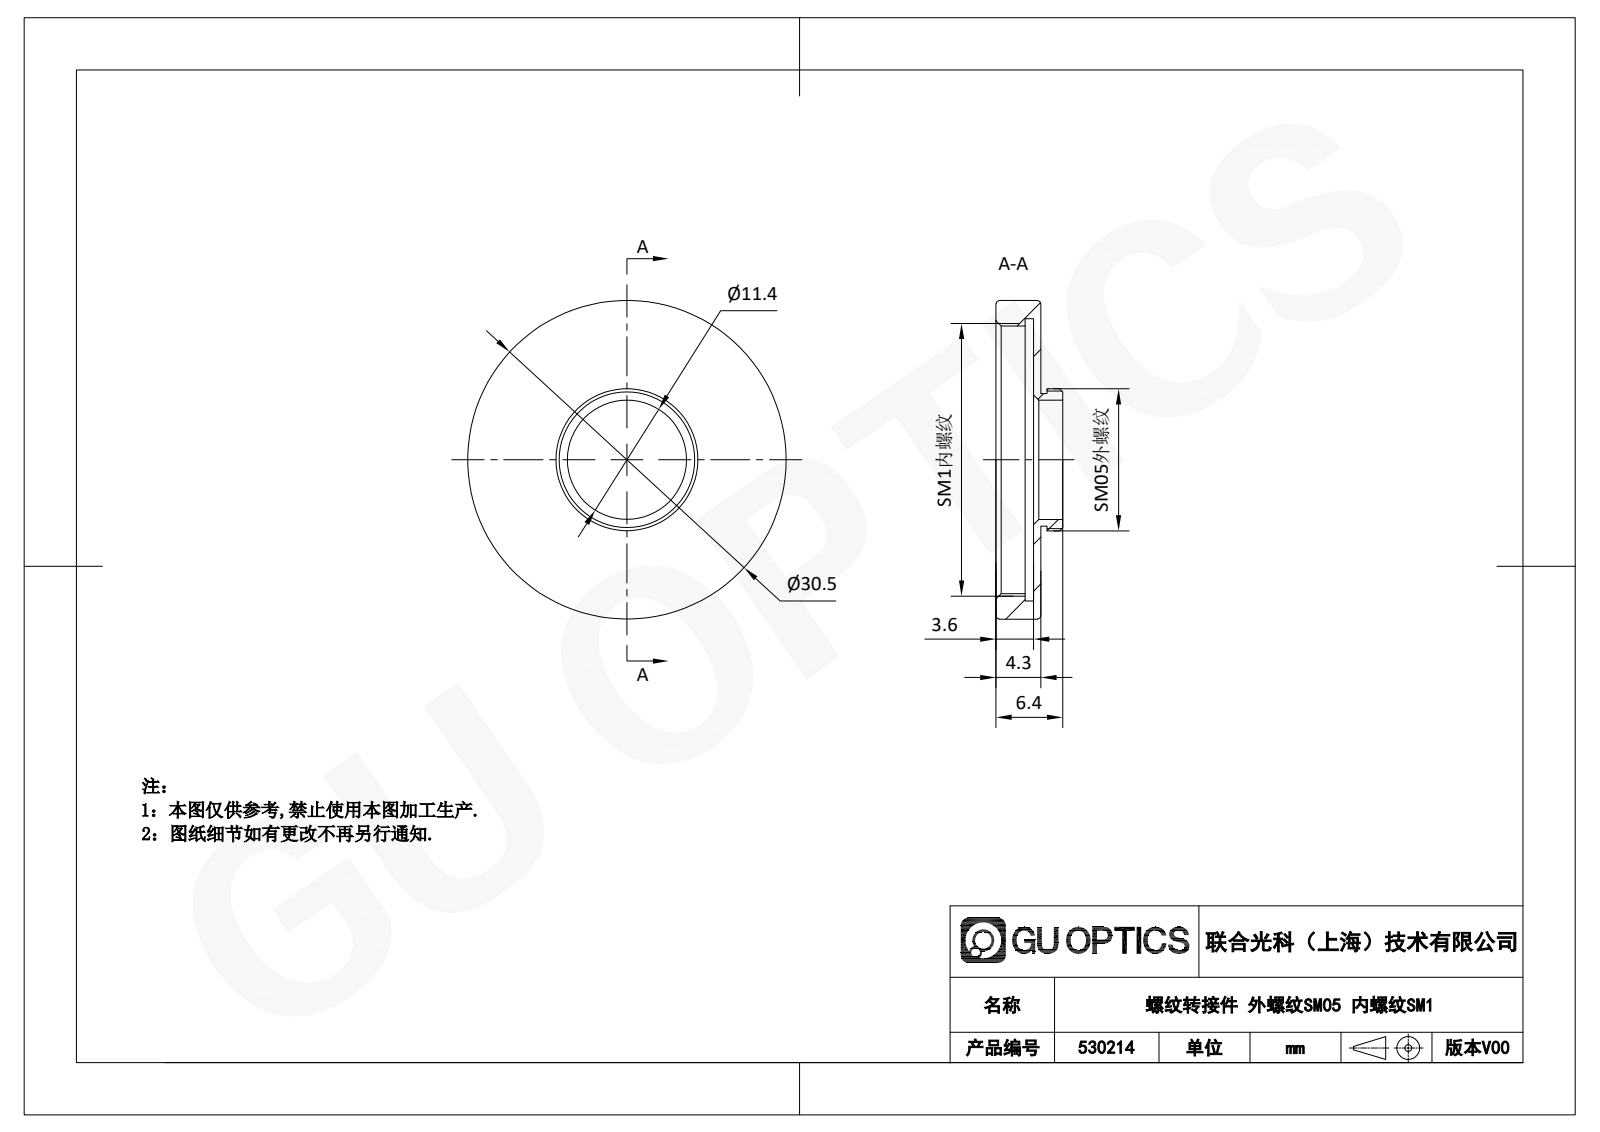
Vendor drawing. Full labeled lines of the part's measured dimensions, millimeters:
Part name (STEP PRODUCT): 530214
STEP written by: SolidWorks 2020 (CONFIG_CONTROL_DESIGN)
Units: millimetres
Bodies: 1 solid, 17 faces (6 planar, 6 cylindrical, 5 other)
Overall size (bounding box): 30.5 × 30.5 × 6.4
Volume: 1 230 mm³ · Surface area: 2 237 mm²
Round holes (diameter × count): ⌀11.4 ×1, ⌀25.6 ×1, ⌀27 ×1
Round bosses / shafts (diameter × count): ⌀30.5 ×1, ⌀13.6 ×1, ⌀12.7 ×1
Main face-to-face distances: 0.7, 3.6, 4.3, 2.8, 1.5, 0.8, 2.1, 6.4, 0.6, 1.3
